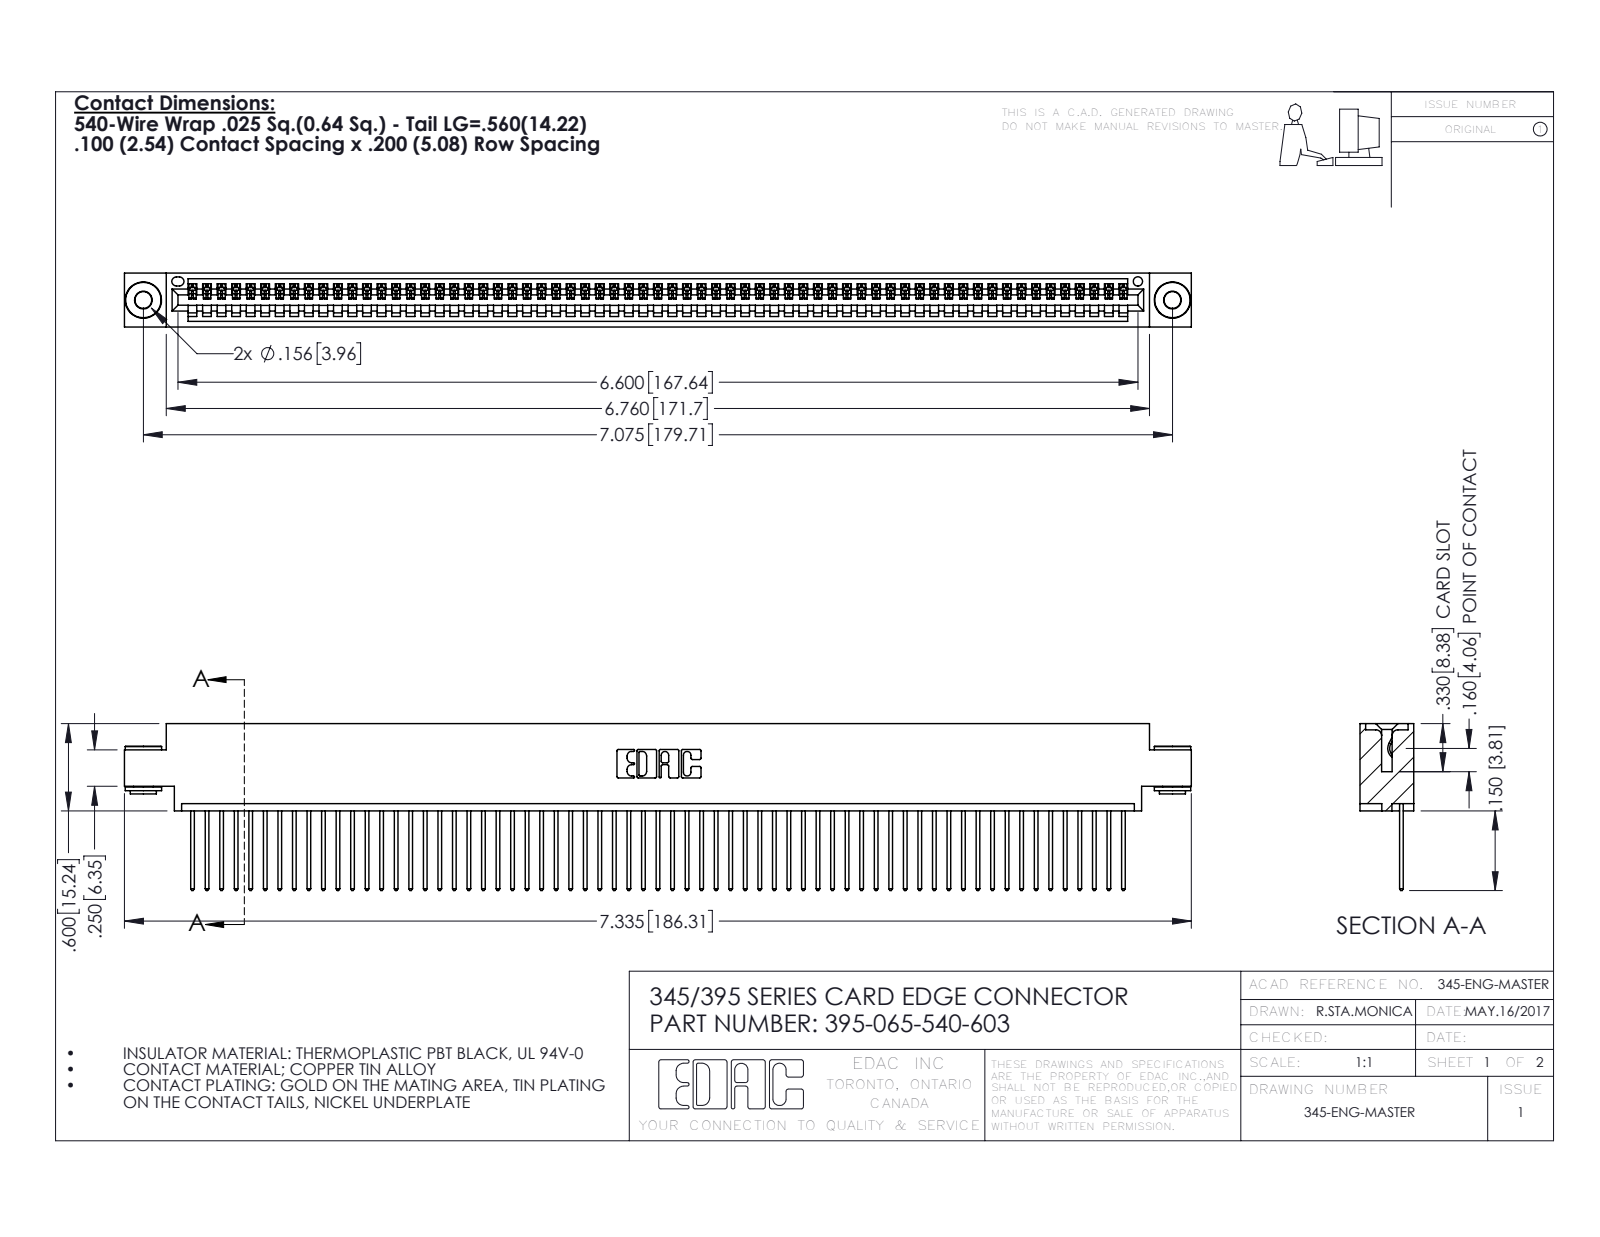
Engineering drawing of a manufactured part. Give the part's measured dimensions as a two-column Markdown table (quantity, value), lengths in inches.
| quantity | value |
| --- | --- |
| part name | 395-065-540-603; 345-250-002_345-250-002-102; 345-292-001_345-293-140; 345 Part_0.170 Offset - 0.156 Dia-TH |
| STEP written by | SolidWorks 2016 (CONFIG_CONTROL_DESIGN) |
| units | inches |
| bodies | 68 solids, 3938 faces (2694 planar, 1236 cylindrical, 8 other) |
| overall size | 7.335 × 1.147 × 0.37 |
| volume | 1.091 in³ |
| surface area | 38.82 in² |
| round holes (diameter × count) | 0.116 × 2, 0.156 × 2, 0.064 × 1 |
| round bosses / shafts (diameter × count) | 0.25 × 2, 0.18 × 2, 0.136 × 2 |
| partial cylindrical surfaces (radius × count) | 0.006 × 130, 0.01 × 130, 0.01 × 22, 0.007 × 6, 0.031 × 6, 0.026 × 3, 0.031 × 2, 0.04 × 2 |
| main face-to-face distances | 0.072, 0.298, 0.37, 0.098, 0.272, 0.025, 0.2, 0.225, 0.175, 0.149 |
| hole center spacings | 0.27, 6.839, 7.075 |
